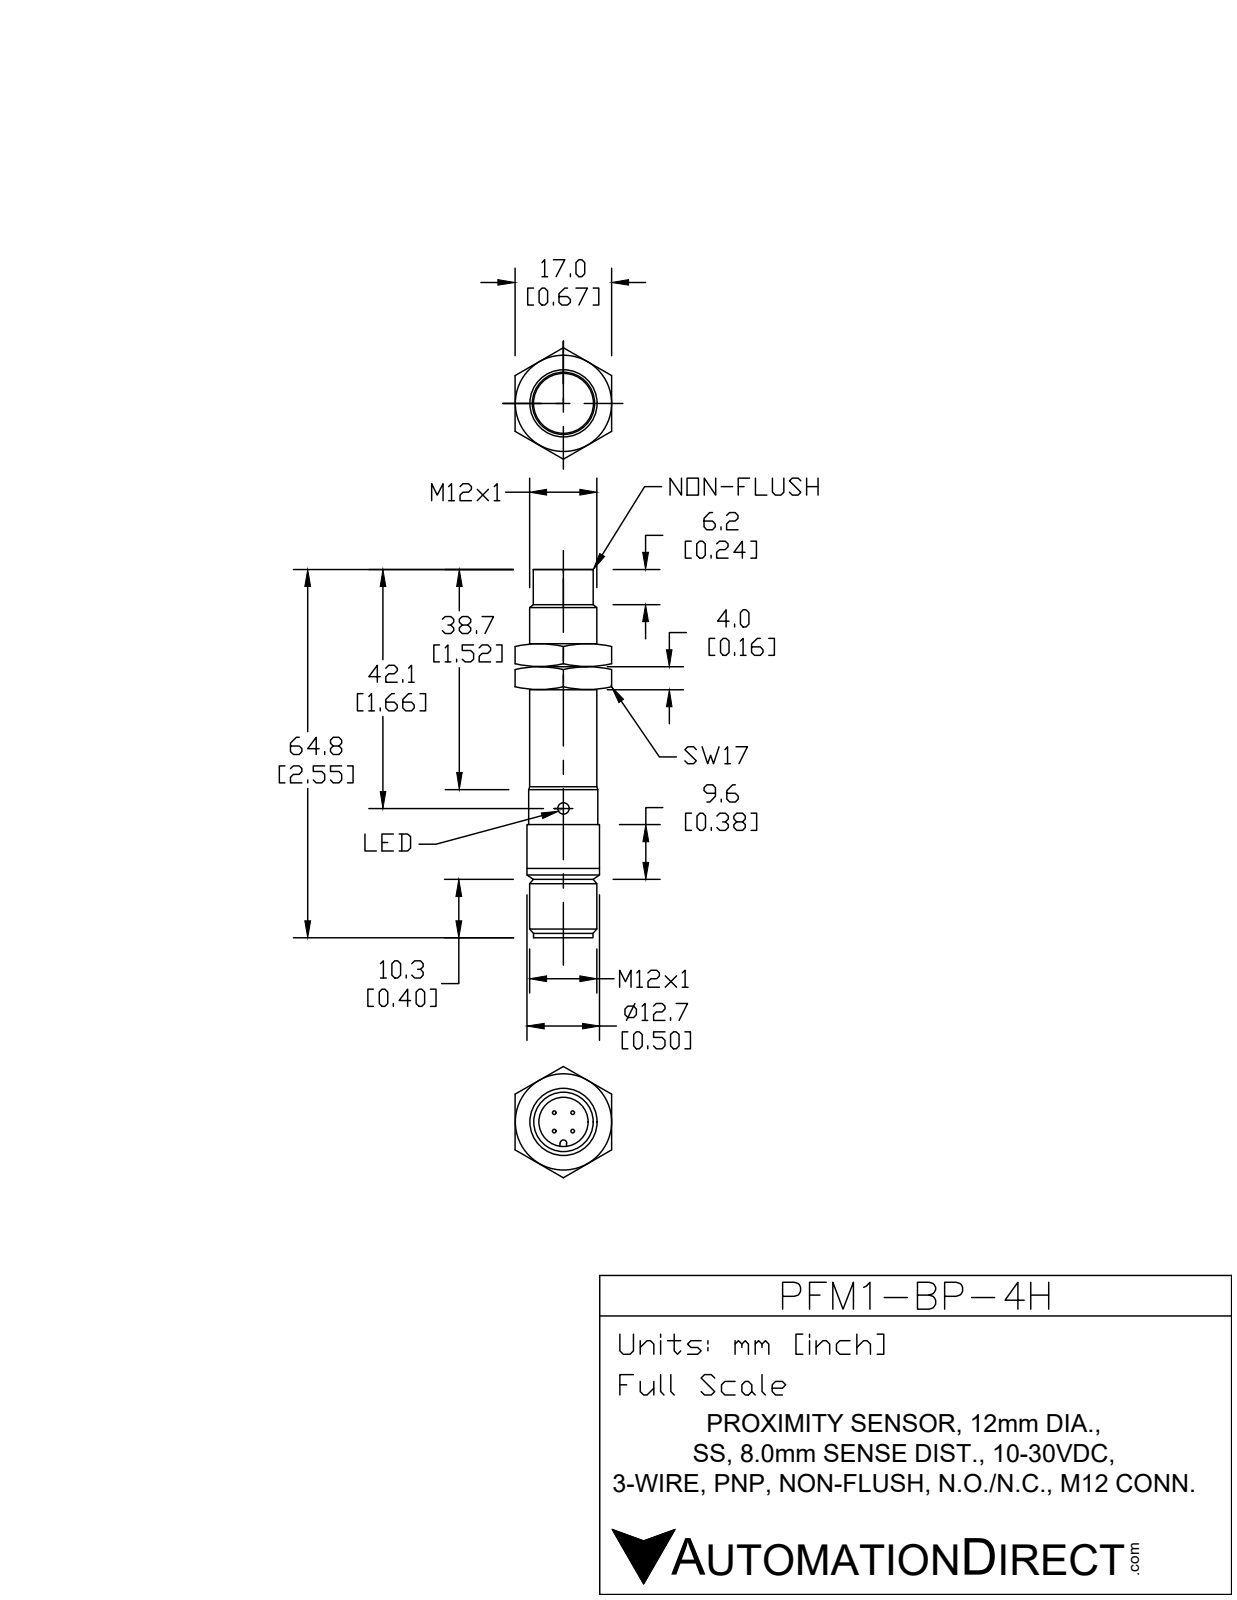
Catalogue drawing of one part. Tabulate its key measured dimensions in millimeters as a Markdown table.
| quantity | value |
| --- | --- |
| part name | PFM1-BP-4H |
| STEP written by | SolidWorks 2017 (AUTOMOTIVE_DESIGN) |
| units | millimeters |
| bodies | 4 solids, 73 faces (11 planar, 36 cylindrical, 26 other) |
| overall size | 64.6 × 12.7 × 12.7 |
| volume | 6 700 mm³ |
| surface area | 4 054 mm² |
| round holes (diameter × count) | 3 × 1, 8.4 × 1, 8.5 × 1, 9.5 × 1 |
| round bosses / shafts (diameter × count) | 1 × 4, 12.7 × 1, 12 × 1, 10.5 × 1, 10 × 1, 9.4 × 1 |
| partial cylindrical surfaces (radius × count) | 0.6 × 1, 5.6 × 1 |
| main face-to-face distances | 46.7, 48.5, 1.8, 6, 52.7, 54.5, 55.7, 49.7, 3, 1.2 |
